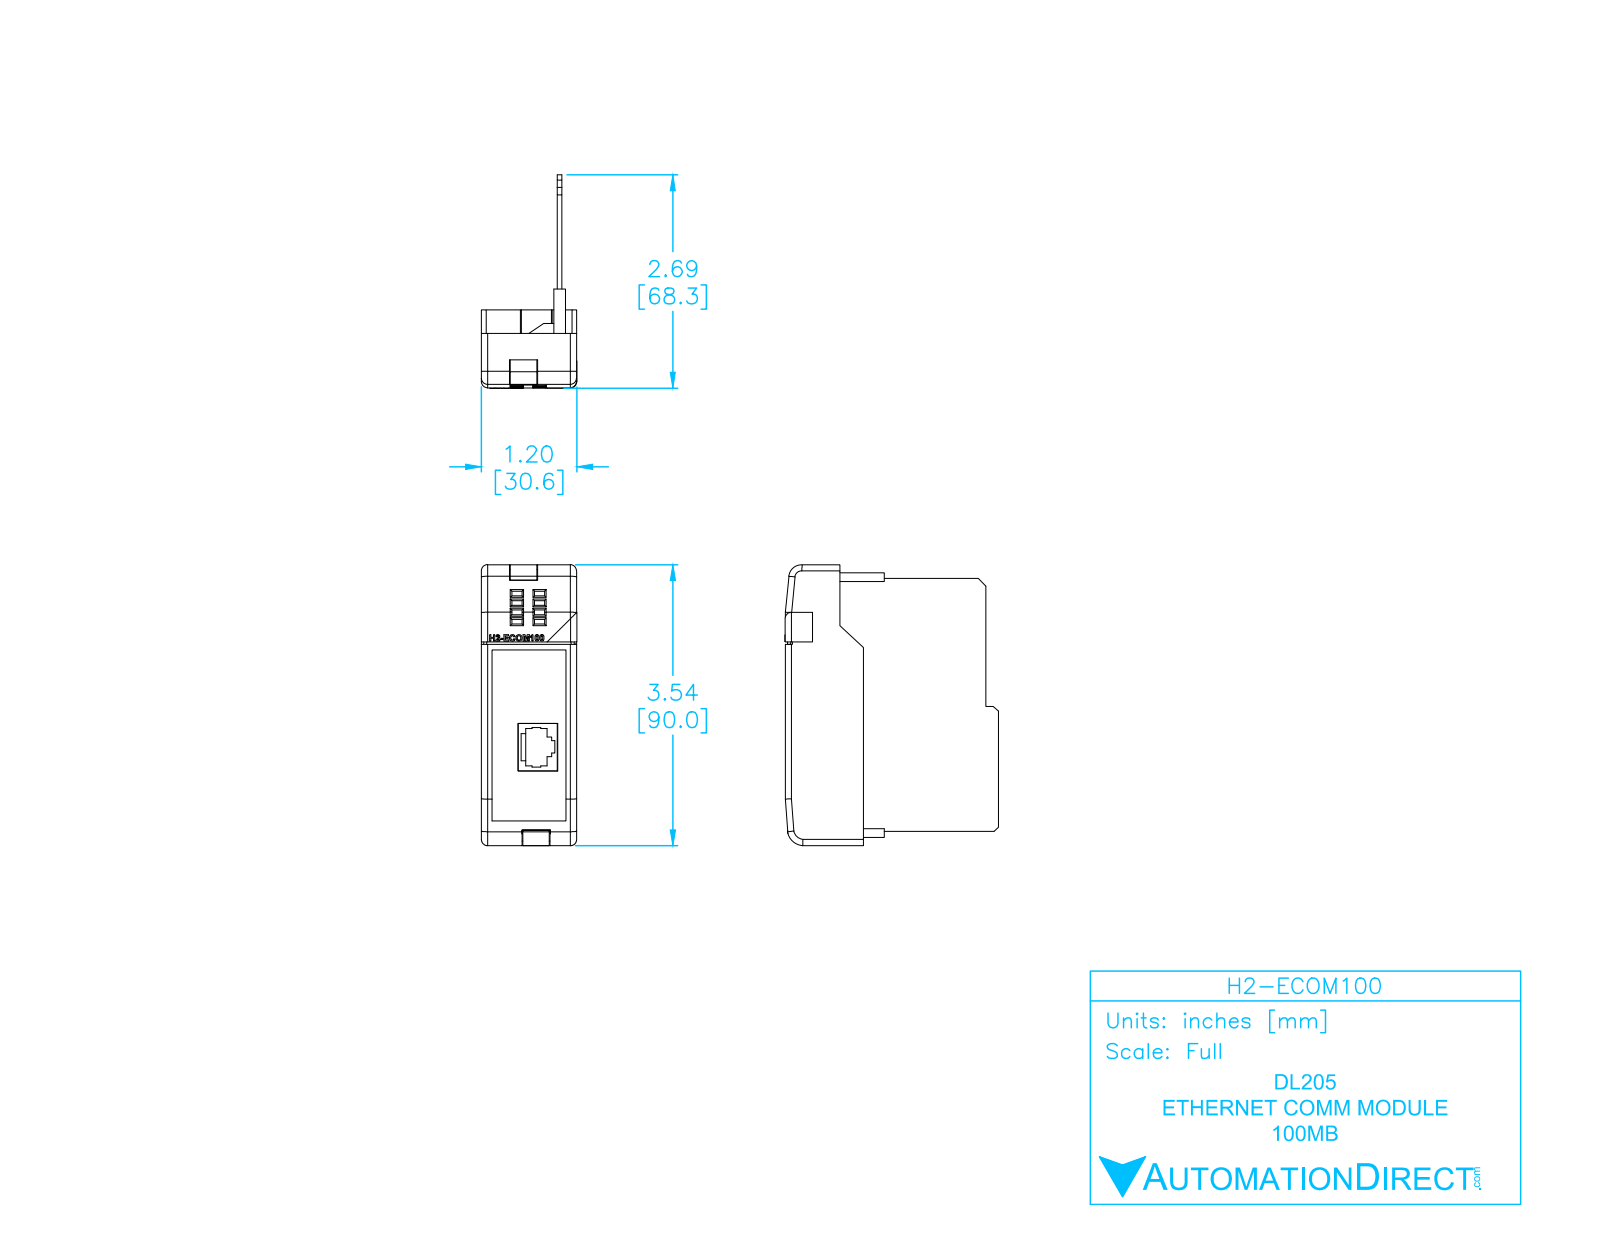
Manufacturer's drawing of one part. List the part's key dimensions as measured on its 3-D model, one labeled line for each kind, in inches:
Part name (STEP PRODUCT): H2-ECOM100
STEP written by: SolidWorks 2009 (AUTOMOTIVE_DESIGN)
Units: inches
Bodies: 2 solids, 418 faces (267 planar, 85 cylindrical, 66 other)
Overall size (bounding box): 3.543 × 2.692 × 1.203
Volume: 1.155 in³ · Surface area: 44.72 in²
Partial cylindrical surfaces — rounded edges, fillets, slot ends (radius × count): R0.02 ×29, R0.079 ×11, R0.01 ×4, R0.039 ×2, R0.103 ×1, R0.149 ×1, R0.162 ×1, R0.208 ×1
Main face-to-face distances: 0.059, 0.186, 0.127, 0.245, 0.02, 0.956, 1.142, 1.015, 1.201, 1.083
